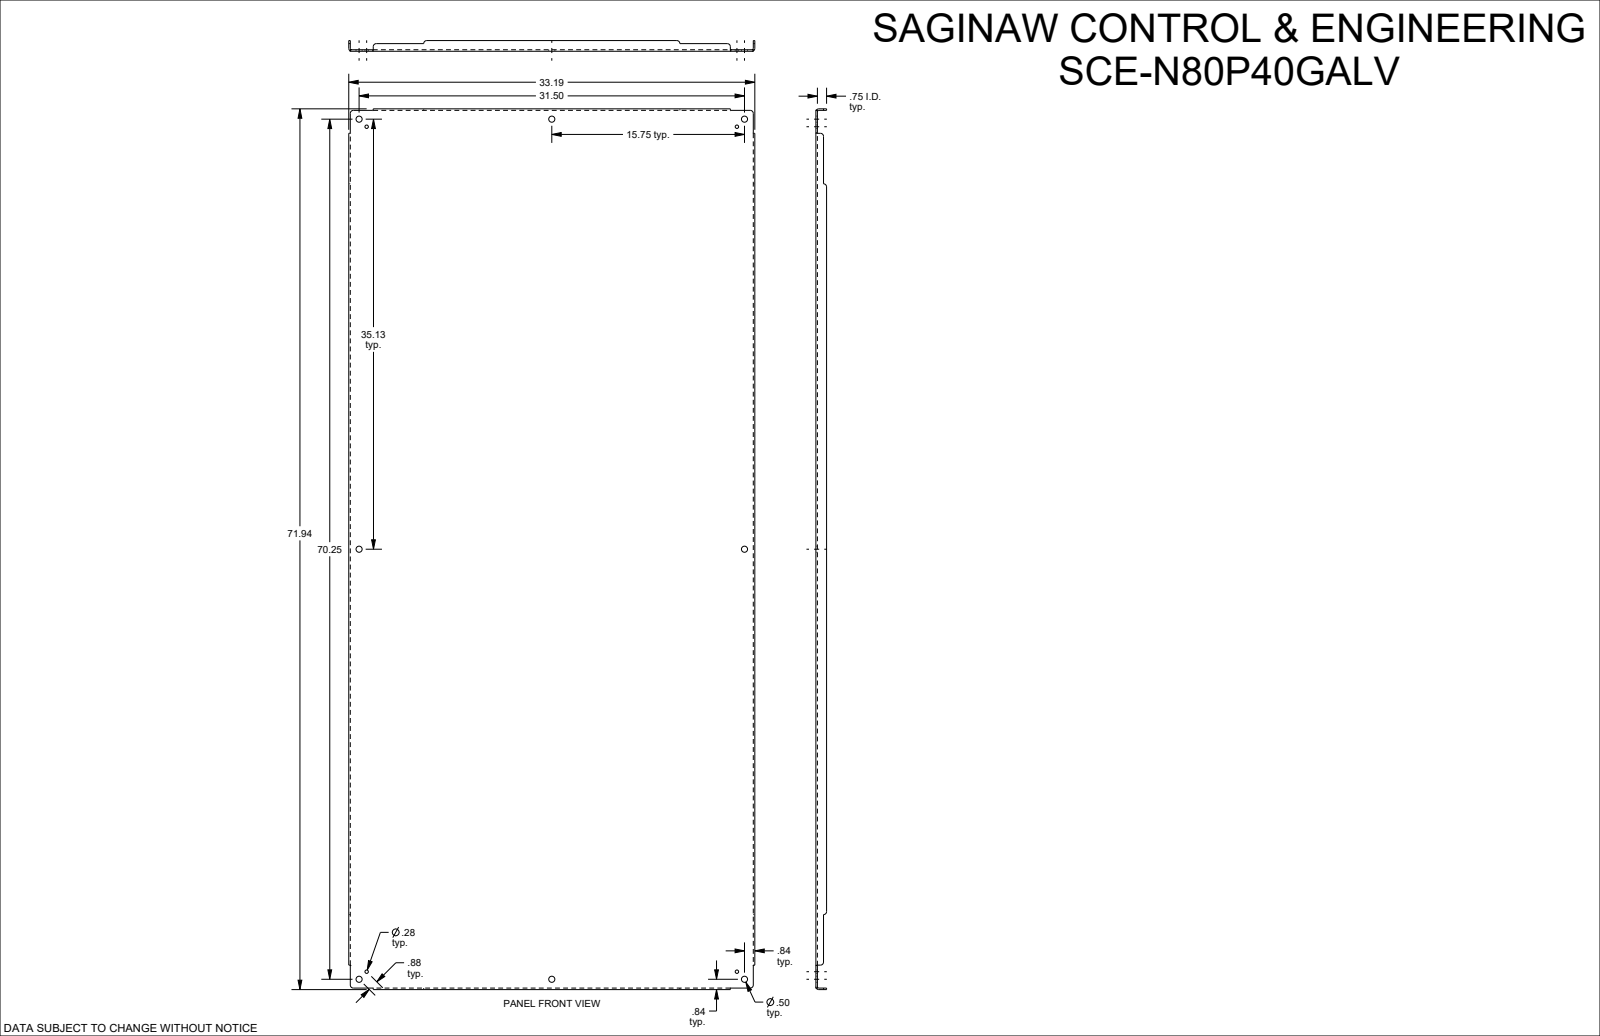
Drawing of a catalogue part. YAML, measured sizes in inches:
part_name: "SCE-N80P40GALV"
step_written_by: "SolidWorks 2023 (AUTOMOTIVE_DESIGN)"
units: inches
bodies: {solids: 1, faces: 122, planar: 46, cylindrical: 52, other: 24}
overall_size: [71.938, 33.188, 0.875]
volume: 313.3
surface_area: 5041
round_holes:
  - {diameter: 0.5, count: 8}
  - {diameter: 0.281, count: 4}
partial_cylinders:
  - {radius: 0.25, count: 12}
  - {radius: 0.112, count: 4}
  - {radius: 0.237, count: 4}
face_to_face_distances: [0.125, 33.063, 32.938, 33.187, 0.125, 71.813, 0.75, 0.875, 71.687, 71.938]
hole_center_spacings: [0.875, 15.144, 15.75, 30.887, 34.512, 35.125, 38.494, 46.307]
